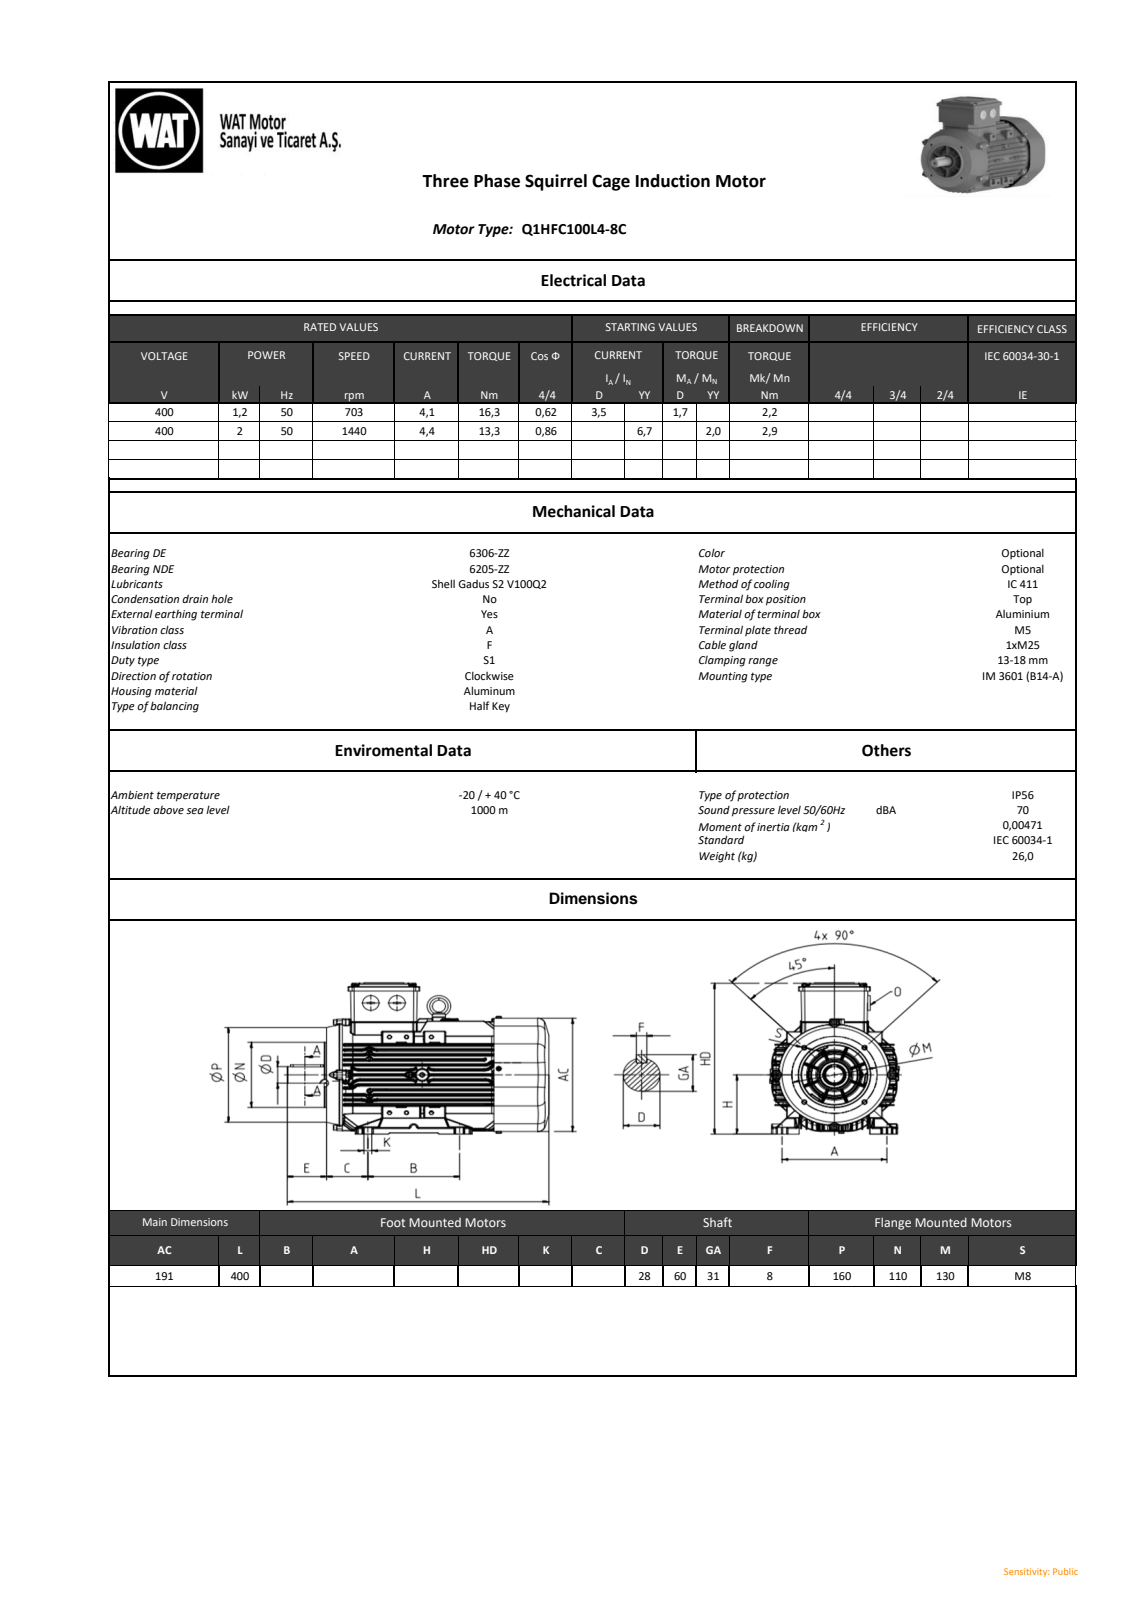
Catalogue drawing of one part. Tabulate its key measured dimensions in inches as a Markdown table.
| quantity | value |
| --- | --- |
| part name | QH series_ 100_B14a_stp_objects |
| STEP written by | SIEMENS PLM Software NX2206.8101 (AUTOMOTIVE_DESIGN) |
| units | inches |
| bodies | 0 solids, 5501 faces (1200 planar, 2176 cylindrical, 2125 other) |
| overall size | 15.721 × 10.023 × 7.785 |
| round holes (diameter × count) | 0.268 × 4, 0.394 × 1, 1.749 × 1, 2.26 × 1, 3.504 × 1, 4.291 × 1, 5.079 × 1, 5.236 × 1 |
| round bosses / shafts (diameter × count) | 0.315 × 8, 0.335 × 4, 0.197 × 4, 0.984 × 3, 4.469 × 1, 4.331 × 1, 3.681 × 1, 2.391 × 1 |
| partial cylindrical surfaces (radius × count) | 0.031 × 669, 0.039 × 490, 0.079 × 91, 0.02 × 88, 0.032 × 50, 0.197 × 40, 0.591 × 26, 1.772 × 16 |
| main face-to-face distances | 0.336, 0.333, 0.333, 3.002, 0.666, 3.679, 1.007, 0.671, 3.019, 2.348 |
| hole center spacings | 2.559, 3.619, 5.118 |
